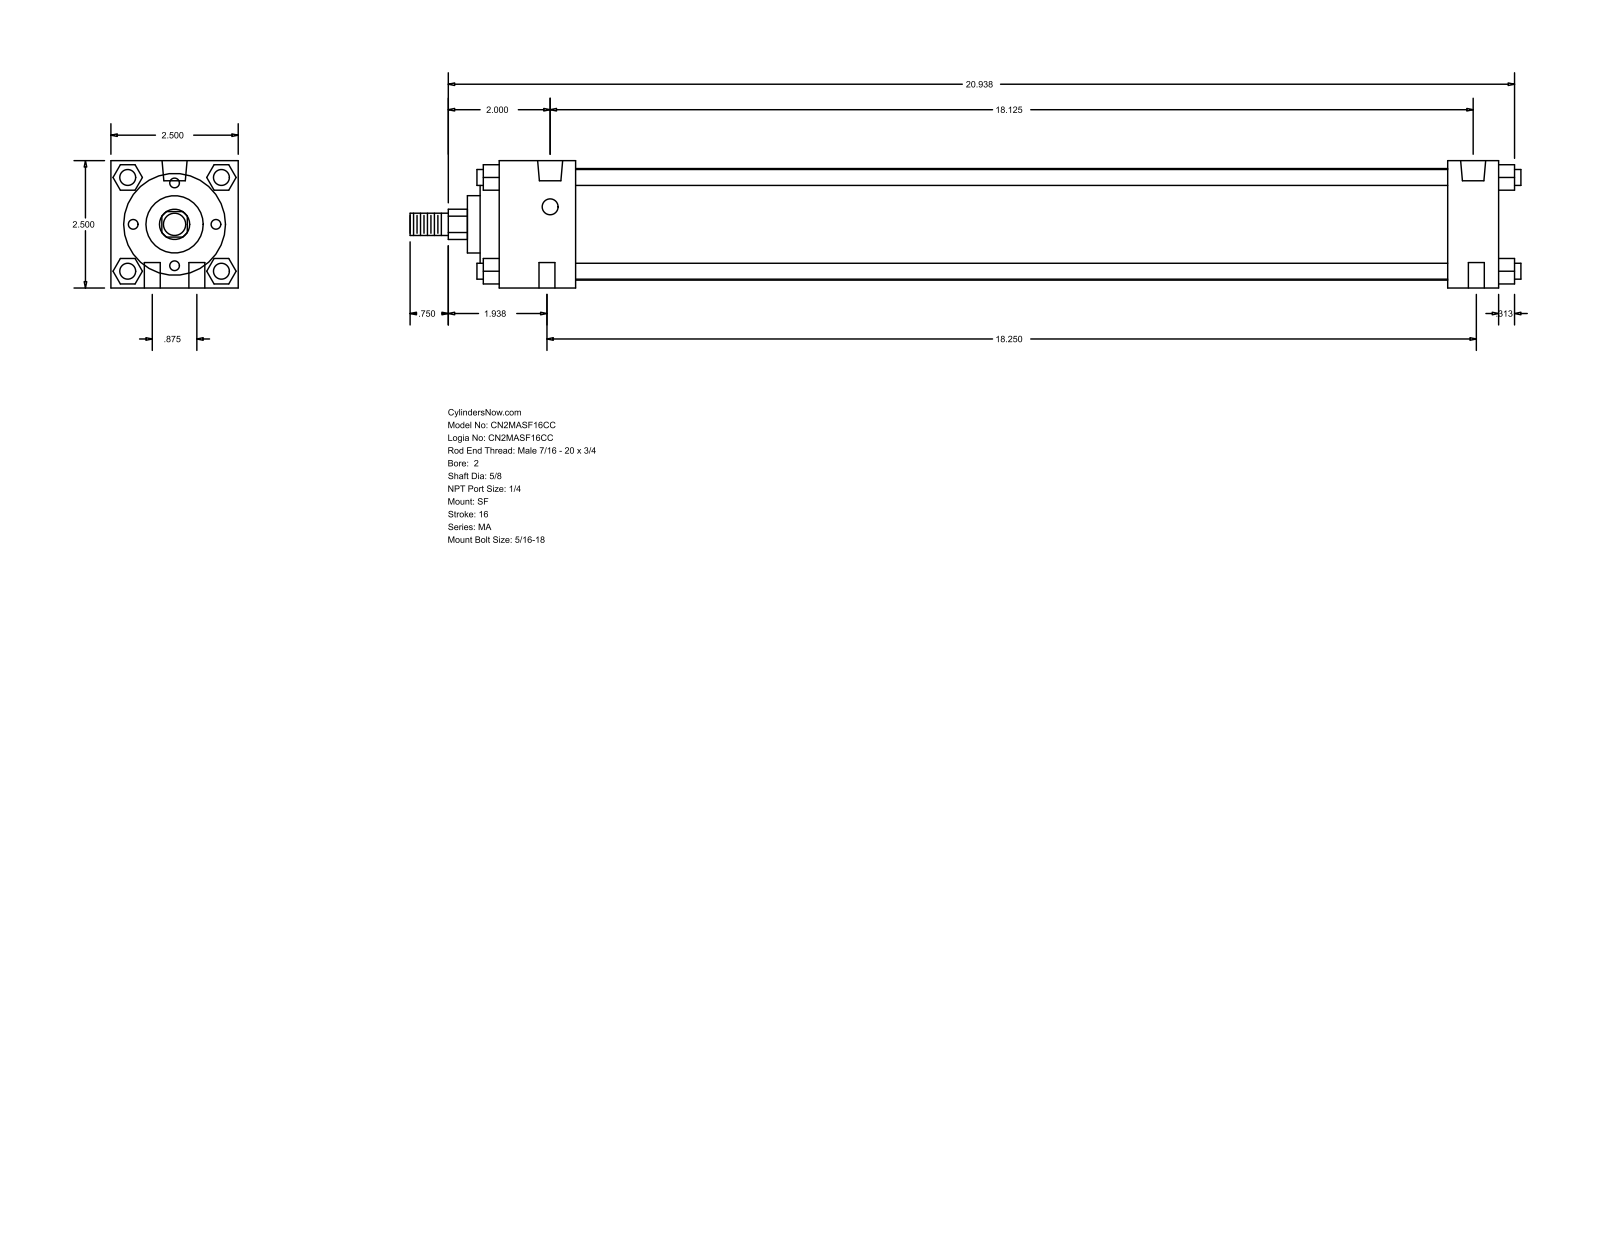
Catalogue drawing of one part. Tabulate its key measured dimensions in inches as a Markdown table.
| quantity | value |
| --- | --- |
| part name | MA_SF__0200_0.625 |
| STEP written by | GSSL Pune (CONFIG_CONTROL_DESIGN) |
| units | inches |
| bodies | 0 solids, 126 faces (95 planar, 31 cylindrical, 0 other) |
| overall size | 21.813 × 2.5 × 2.5 |
| round holes (diameter × count) | 0.313 × 6, 0.492 × 2 |
| round bosses / shafts (diameter × count) | 0.313 × 4, 2.19 × 1, 2 × 1, 1.125 × 1, 0.625 × 1, 0.437 × 1 |
| partial cylindrical surfaces (radius × count) | 0.297 × 1 |
| main face-to-face distances | 2.5, 1, 0.5, 1.5, 19.625, 18.625, 17.125, 18.125, 0.375, 1.875 |
| hole center spacings | 0.442, 0.875, 18.125, 18.193, 18.193, 18.25, 18.271 |
